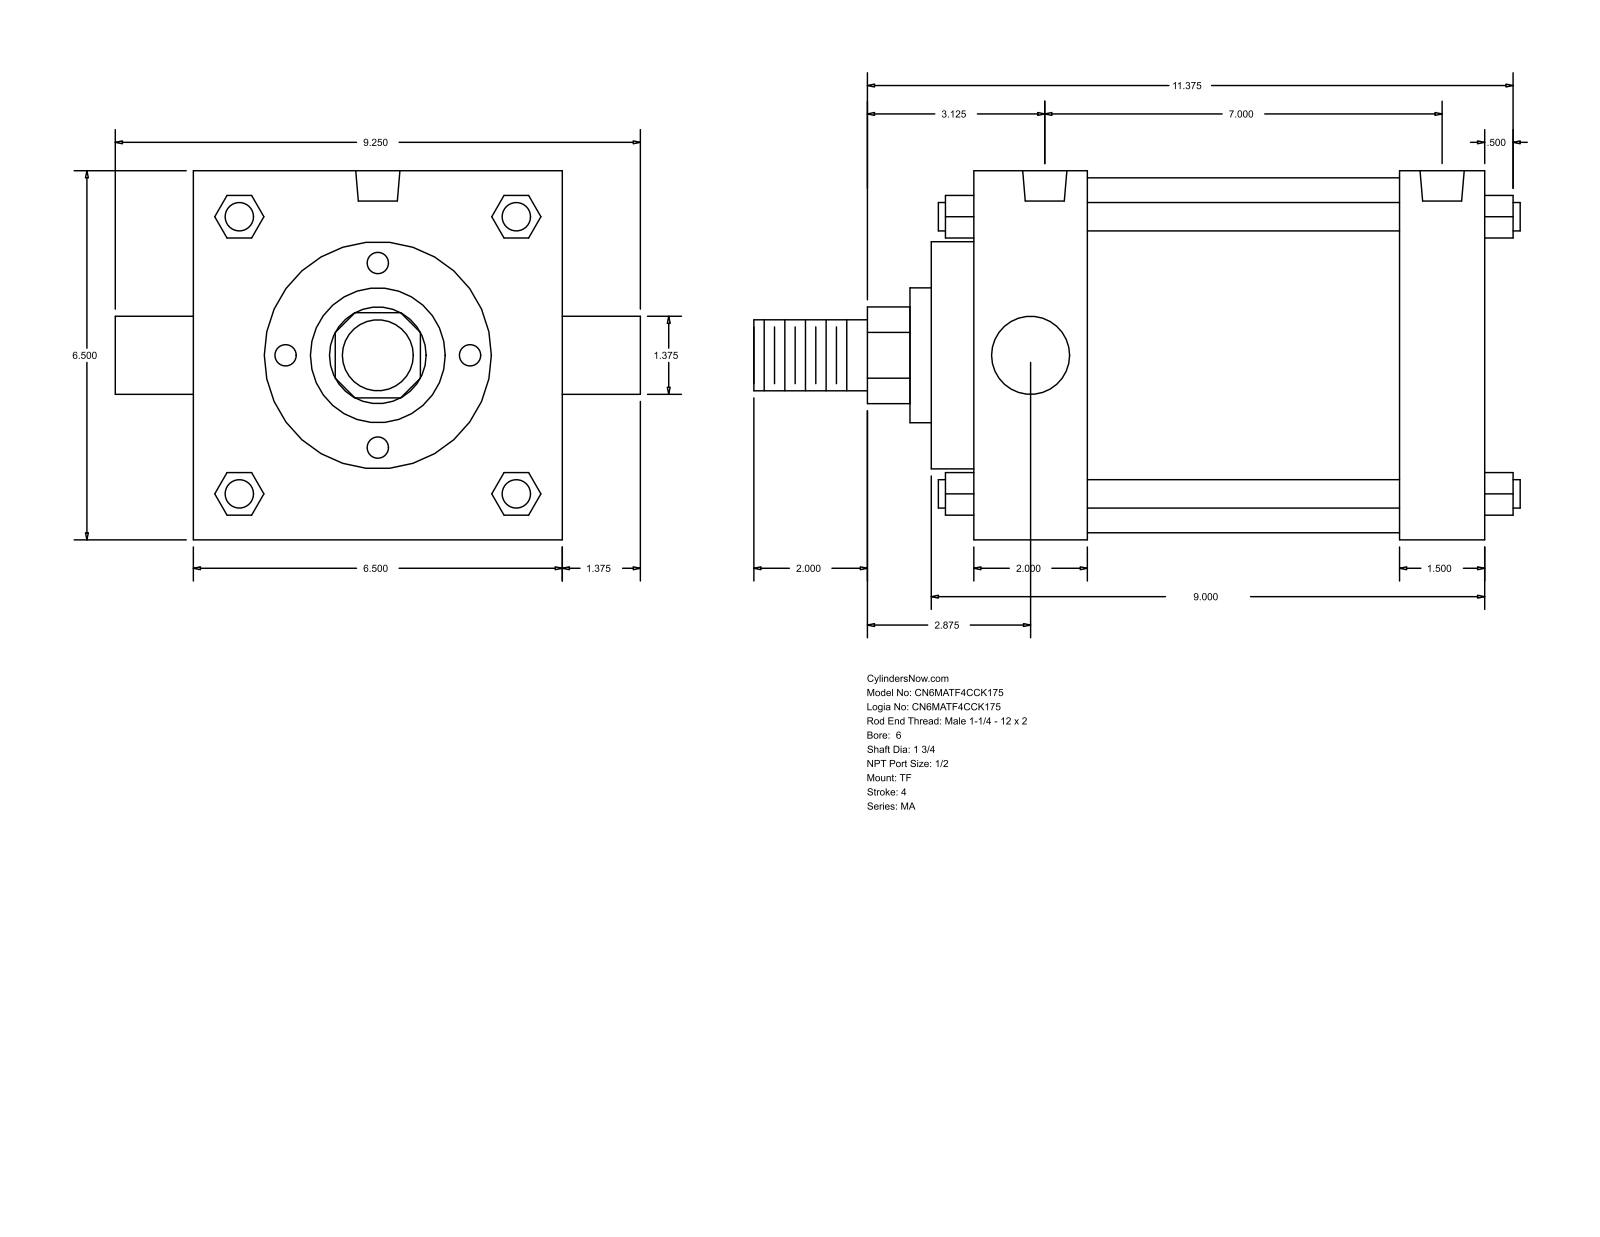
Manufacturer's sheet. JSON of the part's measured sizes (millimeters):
{"part_name": "MA_TF__0600_1.75", "step_written_by": "GSSL Pune (CONFIG_CONTROL_DESIGN)", "units": "millimeters", "bodies": {"solids": 0, "faces": 122, "planar": 93, "cylindrical": 29, "other": 0}, "overall_size": [342.9, 234.95, 165.1], "round_holes": [[17.46, 3], [19.77, 2]], "round_bosses_or_shafts": [[12.7, 4], [158.75, 1], [101.6, 1], [60.33, 1], [44.45, 1], [34.92, 1], [31.75, 1]], "partial_cylinders_radius": [[21.63, 1]], "face_to_face_distances": [165.1, 228.61, 19.05, 50.8, 177.81, 190.5, 139.7, 38.11, 69.85, 209.55], "hole_center_spacings": [177.8]}
